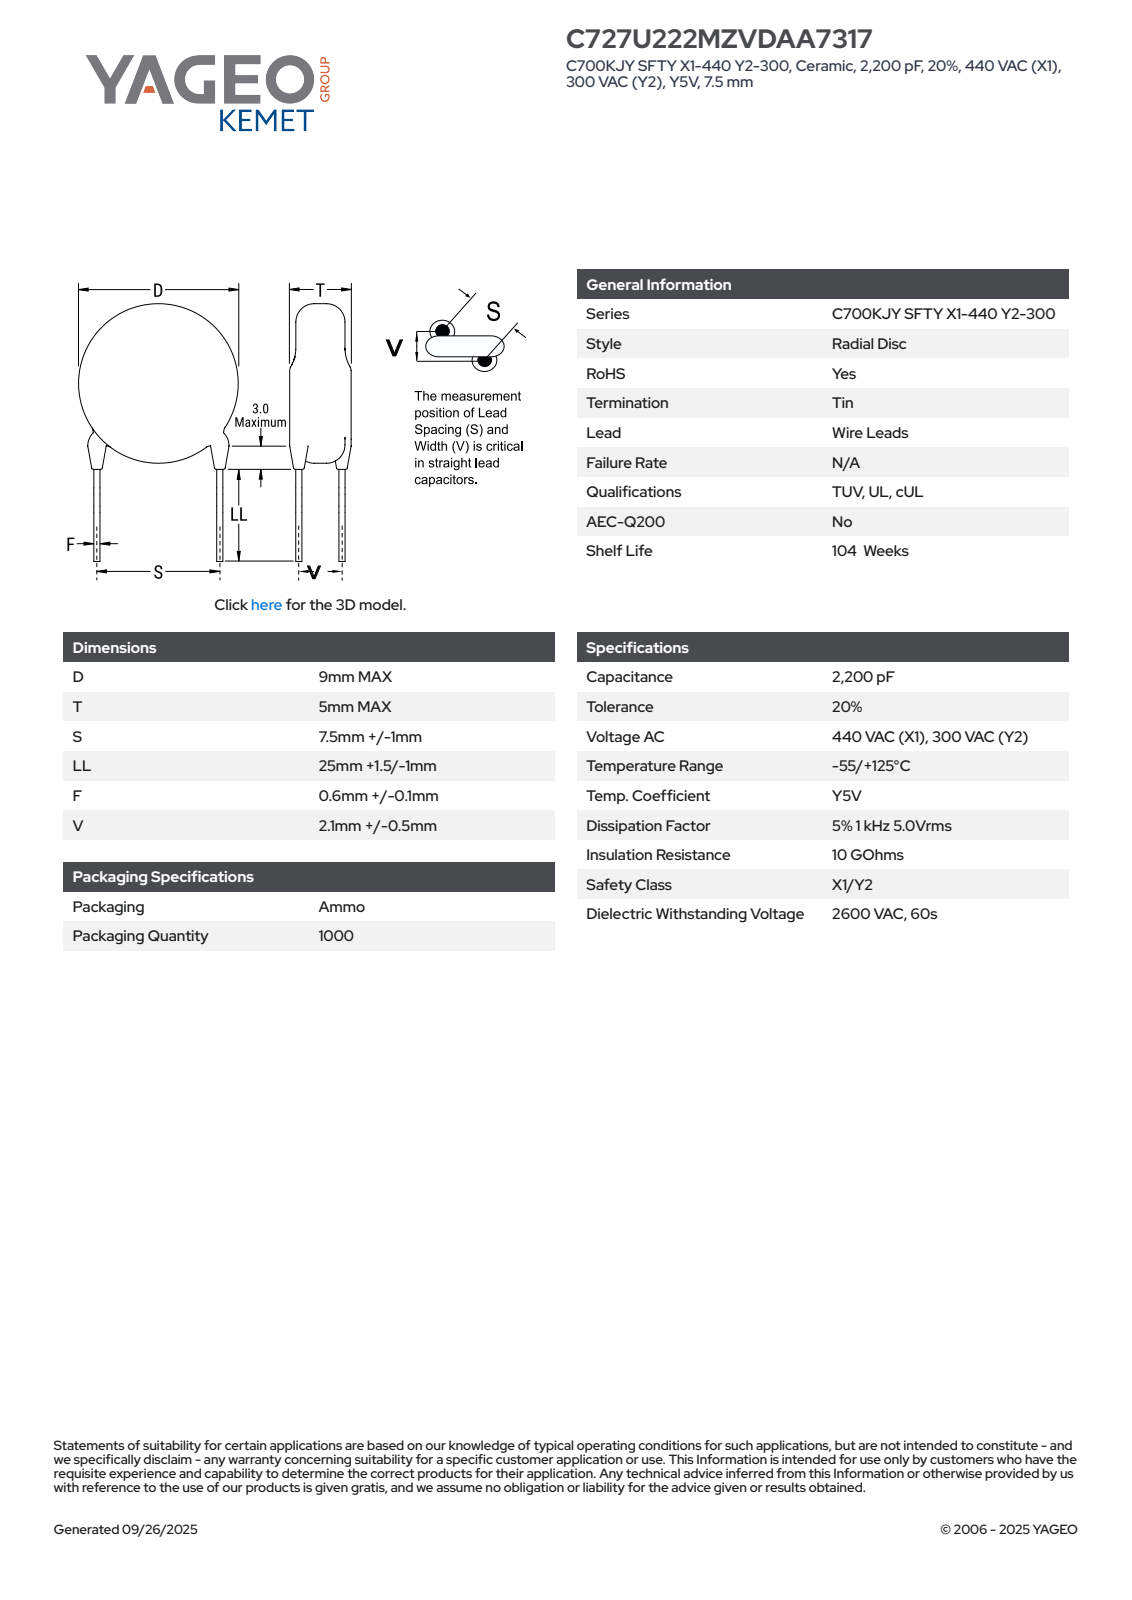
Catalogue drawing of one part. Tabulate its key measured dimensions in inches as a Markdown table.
| quantity | value |
| --- | --- |
| part name | CCD_KST_9X5_D9T5S7.6LL26.5F0.7V2.1 |
| STEP written by | SolidWorks 2021 (AUTOMOTIVE_DESIGN) |
| units | inches |
| bodies | 4 solids, 80 faces (63 planar, 13 cylindrical, 4 other) |
| overall size | 1.449 × 0.354 × 0.197 |
| volume | 0.02 in³ |
| surface area | 0.606 in² |
| round bosses / shafts (diameter × count) | 0.047 × 2, 0.028 × 2, 0.354 × 1 |
| partial cylindrical surfaces (radius × count) | 0.024 × 2 |
| main face-to-face distances | 0.197, 1.043, 0.042, 1.296, 0.253, 1.254, 0.211, 0.172, 0.016, 0.034 |
